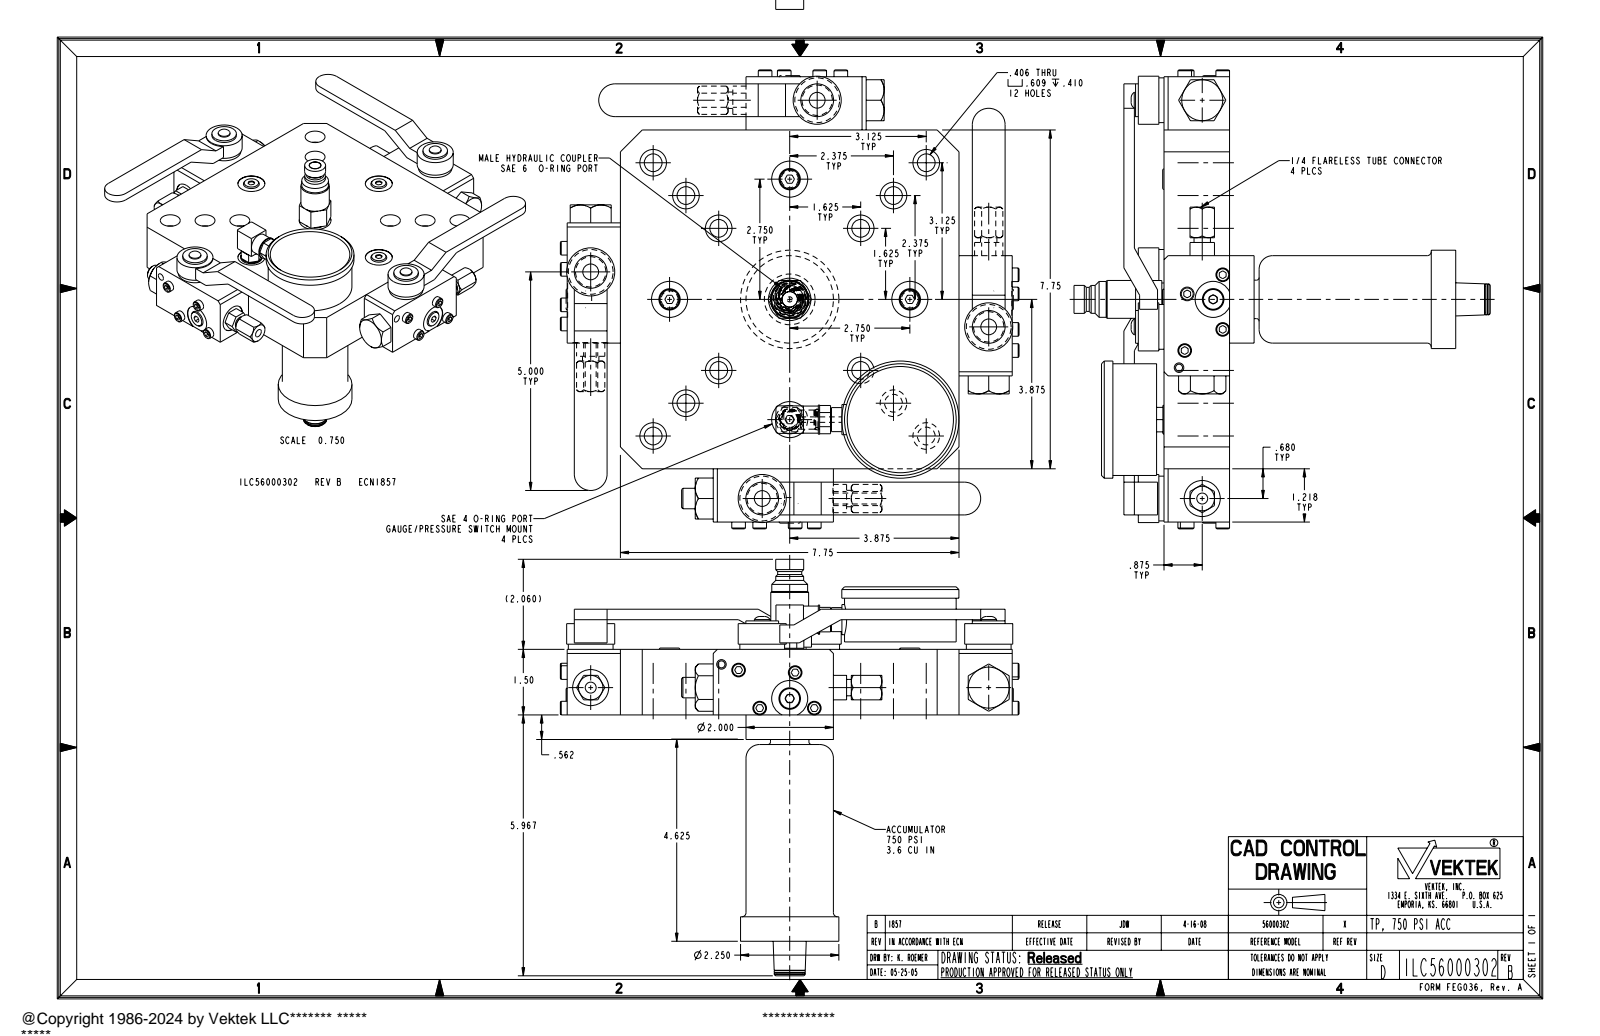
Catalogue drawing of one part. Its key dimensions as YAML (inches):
part_name: "ILC56000302_PLATE; ILC56000302_70101703; ILC56000302_70101700; ILC56000302_301621444 (+2 more)"
step_written_by: "PRO/ENGINEER BY PARAMETRIC TECHNOLOGY CORPORATION, 2007460 (AUTOMOTIVE_DESIGN_CC2)"
units: inches
bodies: {solids: 8, faces: 1332, planar: 611, cylindrical: 443, other: 278}
overall_size: [10.499, 10.499, 9.527]
volume: 135.6
surface_area: 467.1
round_holes:
  - {diameter: 0.218, count: 22}
  - {diameter: 0.159, count: 16}
  - {diameter: 0.406, count: 12}
  - {diameter: 0.609, count: 12}
  - {diameter: 0.392, count: 10}
  - {diameter: 0.825, count: 10}
  - {diameter: 0.188, count: 6}
  - {diameter: 0.5, count: 6}
  - {diameter: 0.25, count: 4}
  - {diameter: 0.694, count: 4}
  - {diameter: 0.12, count: 1}
  - {diameter: 0.125, count: 1}
round_bosses_or_shafts:
  - {diameter: 0.312, count: 16}
  - {diameter: 0.437, count: 8}
  - {diameter: 0.75, count: 5}
  - {diameter: 1.1, count: 4}
  - {diameter: 1.024, count: 4}
  - {diameter: 0.375, count: 4}
  - {diameter: 0.361, count: 4}
  - {diameter: 0.377, count: 2}
partial_cylinders:
  - {radius: 0.12, count: 4}
  - {radius: 0.375, count: 4}
  - {radius: 0.05, count: 2}
face_to_face_distances: [1.5, 7.75, 1.218, 8.968, 2.418, 0.918, 2.178, 0.678, 0.24, 0.75]
hole_center_spacings: [0.607, 1.061, 1.065, 1.976, 2.404, 3.148, 4.069, 4.667]
